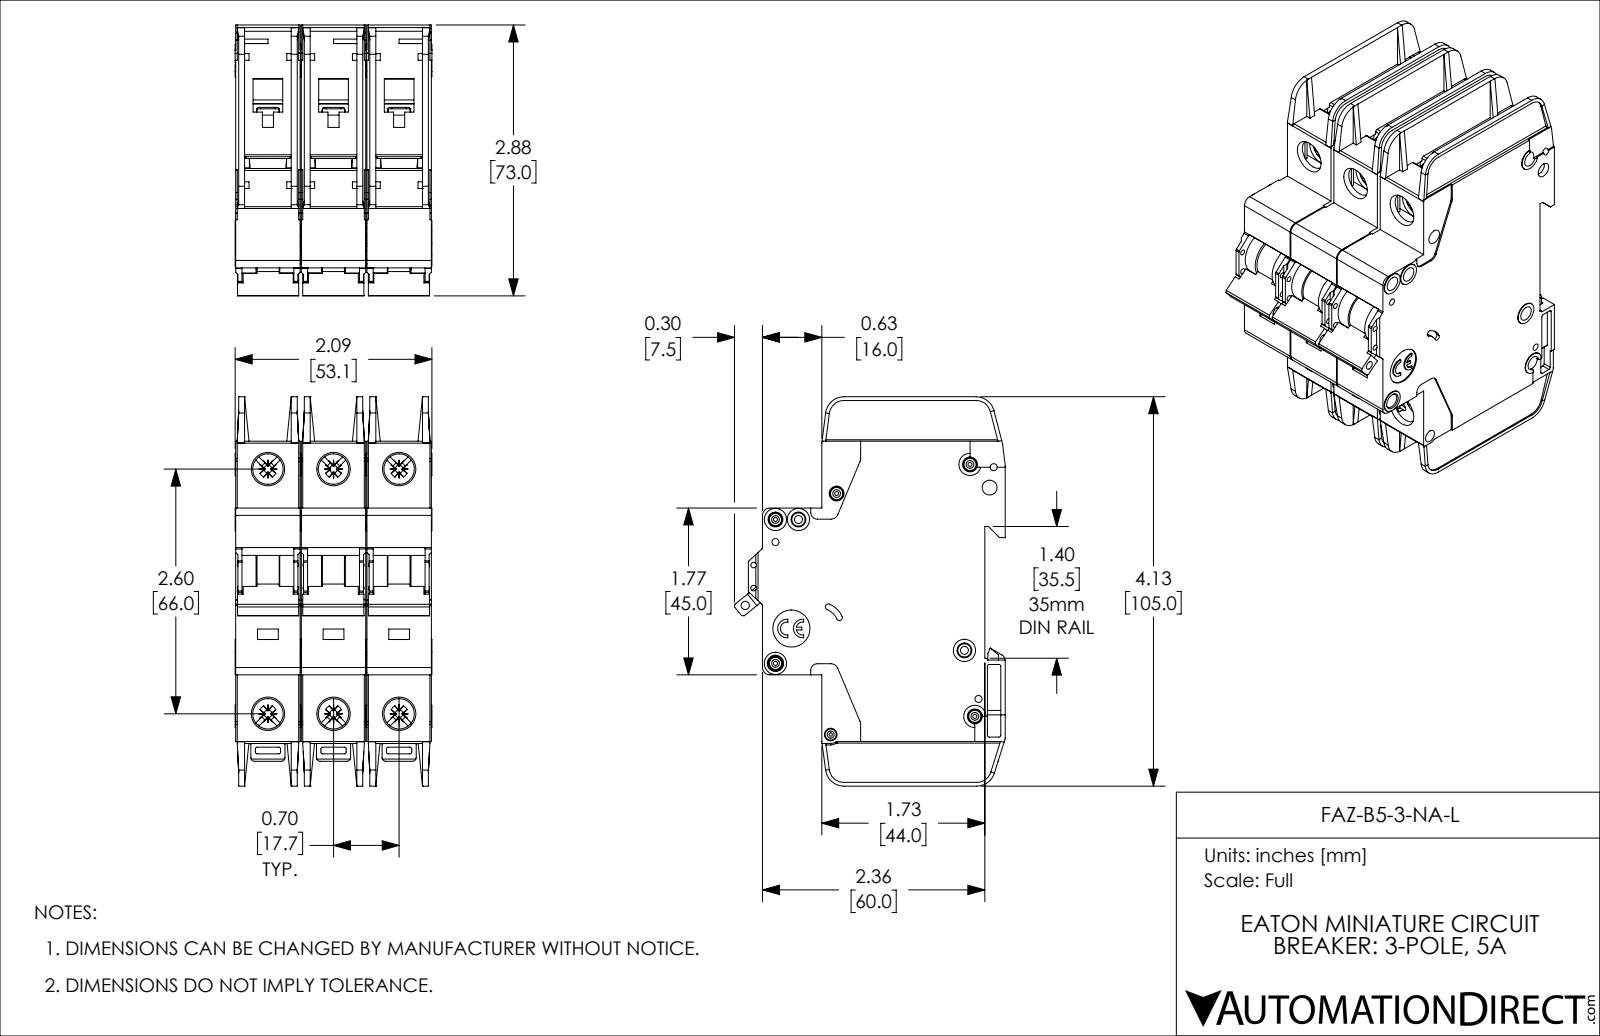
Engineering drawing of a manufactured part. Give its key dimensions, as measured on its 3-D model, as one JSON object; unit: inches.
{"part_name": "FAZ-B5-3-NA-L", "step_written_by": "SolidWorks 2019 (AUTOMOTIVE_DESIGN)", "units": "inches", "bodies": {"solids": 3, "faces": 3381, "planar": 2013, "cylindrical": 1071, "other": 297}, "overall_size": [4.134, 2.876, 2.091], "volume_in3": 14.05, "surface_area_in2": 123, "round_holes": [[0.157, 8], [0.323, 6], [0.043, 5], [0.075, 4], [0.059, 2], [0.085, 2], [0.035, 1], [0.089, 1], [0.098, 1], [0.134, 1], [0.394, 1]], "round_bosses_or_shafts": [[0.13, 5], [0.236, 4], [0.118, 4], [0.098, 3]], "partial_cylinders_radius": [[0.02, 72], [0.016, 30], [0.039, 18], [0.043, 12], [0.079, 12], [0.008, 6], [0.01, 6], [0.028, 6]], "face_to_face_distances": [0.697, 0.047, 1.394, 0.685, 0.591, 1.382, 0.744, 0.65, 0.106, 0.094], "hole_center_spacings": [0.697, 2.69, 2.598, 0.244, 0.537, 0.87, 1.394, 2.948]}
